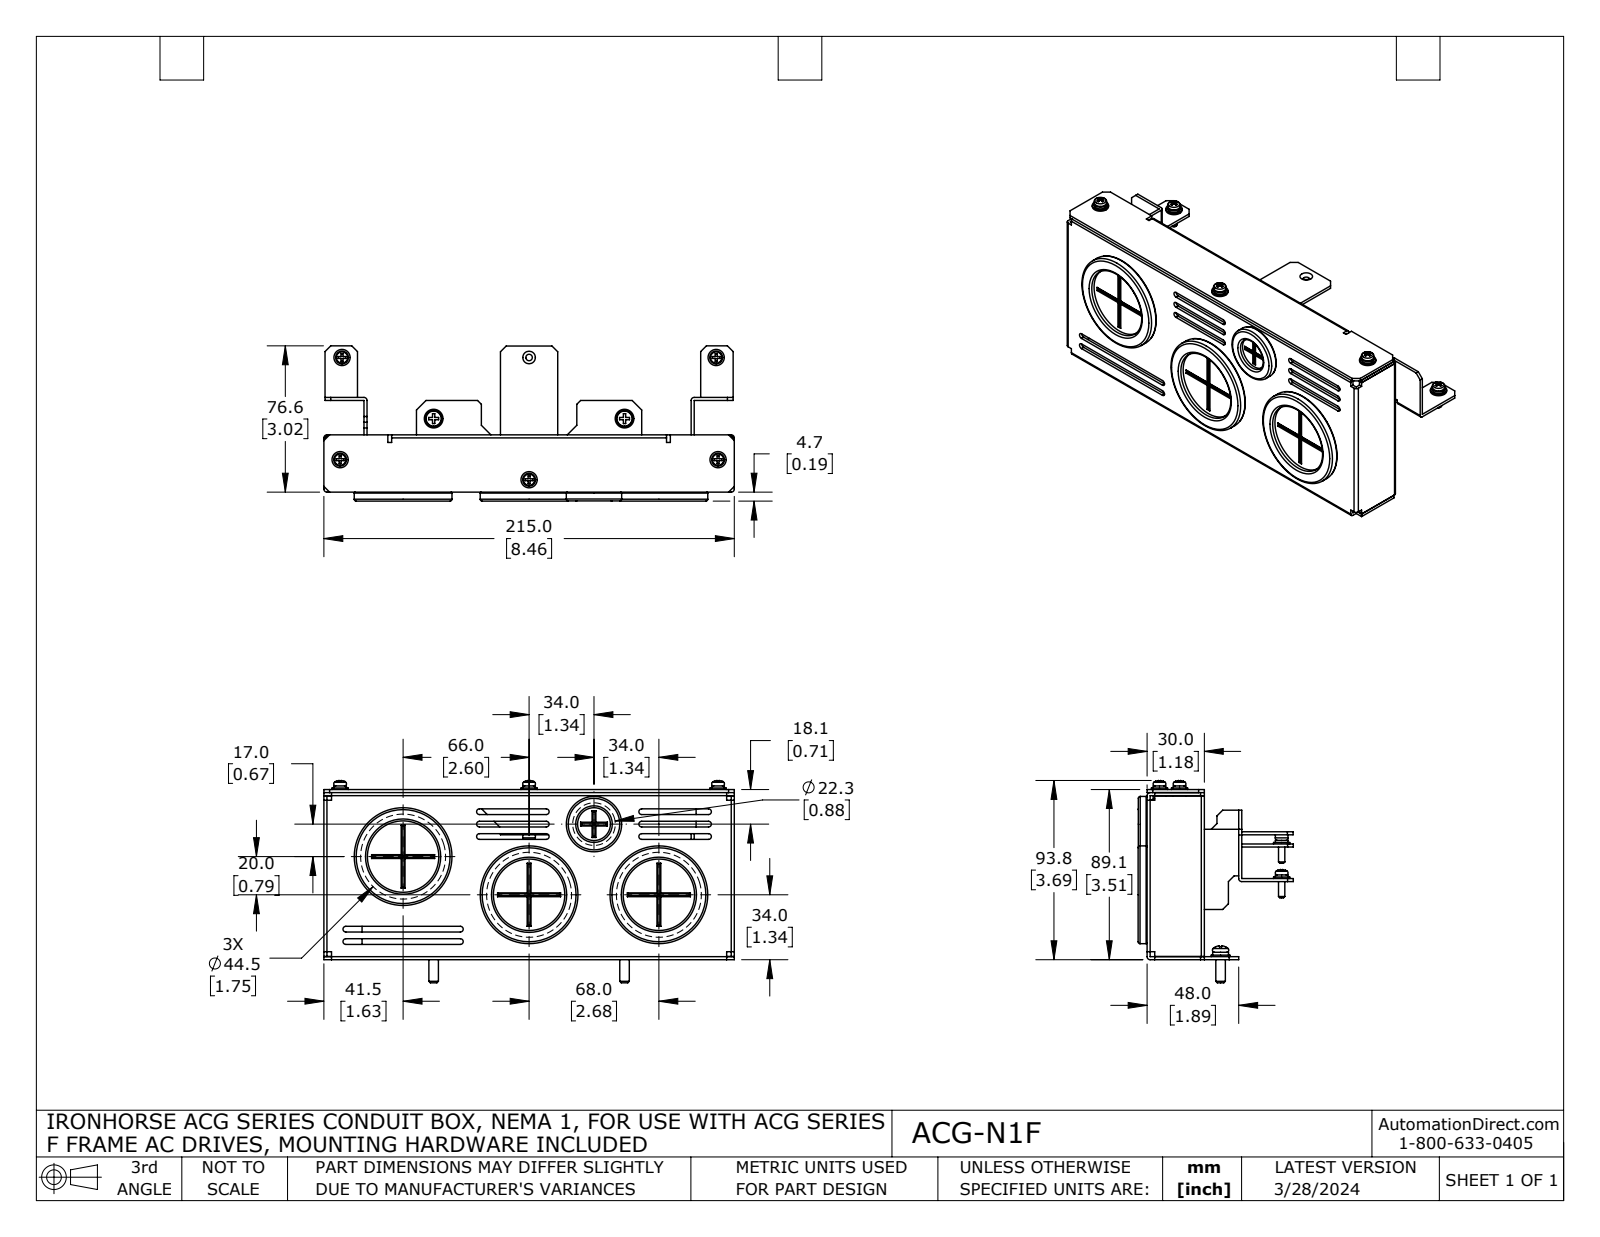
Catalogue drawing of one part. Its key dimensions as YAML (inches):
part_name: "ACG-N1F"
step_written_by: "SolidWorks 2021 (AUTOMOTIVE_DESIGN)"
units: inches
bodies: {solids: 15, faces: 704, planar: 375, cylindrical: 224, other: 105}
overall_size: [8.465, 4.171, 3.201]
volume: 6.881
surface_area: 197.5
round_holes:
  - {diameter: 0.197, count: 5}
  - {diameter: 0.126, count: 4}
  - {diameter: 0.134, count: 4}
  - {diameter: 1.472, count: 3}
  - {diameter: 1.752, count: 3}
  - {diameter: 1.898, count: 3}
  - {diameter: 0.236, count: 2}
  - {diameter: 0.677, count: 1}
  - {diameter: 0.878, count: 1}
  - {diameter: 1.024, count: 1}
round_bosses_or_shafts:
  - {diameter: 0.335, count: 5}
  - {diameter: 0.259, count: 5}
  - {diameter: 0.13, count: 5}
  - {diameter: 0.26, count: 4}
  - {diameter: 0.118, count: 4}
  - {diameter: 2.016, count: 3}
  - {diameter: 1.858, count: 3}
  - {diameter: 1.724, count: 3}
partial_cylinders:
  - {radius: 0.02, count: 28}
  - {radius: 0.059, count: 16}
  - {radius: 0.063, count: 14}
  - {radius: 0.197, count: 2}
face_to_face_distances: [0.063, 3.445, 1.118, 3.382, 1.055, 0.031, 3.508, 1.181, 0.126, 8.402]
hole_center_spacings: [2.107, 2.337, 0.984, 1.978, 2.271, 3.841, 3.858, 3.92]
